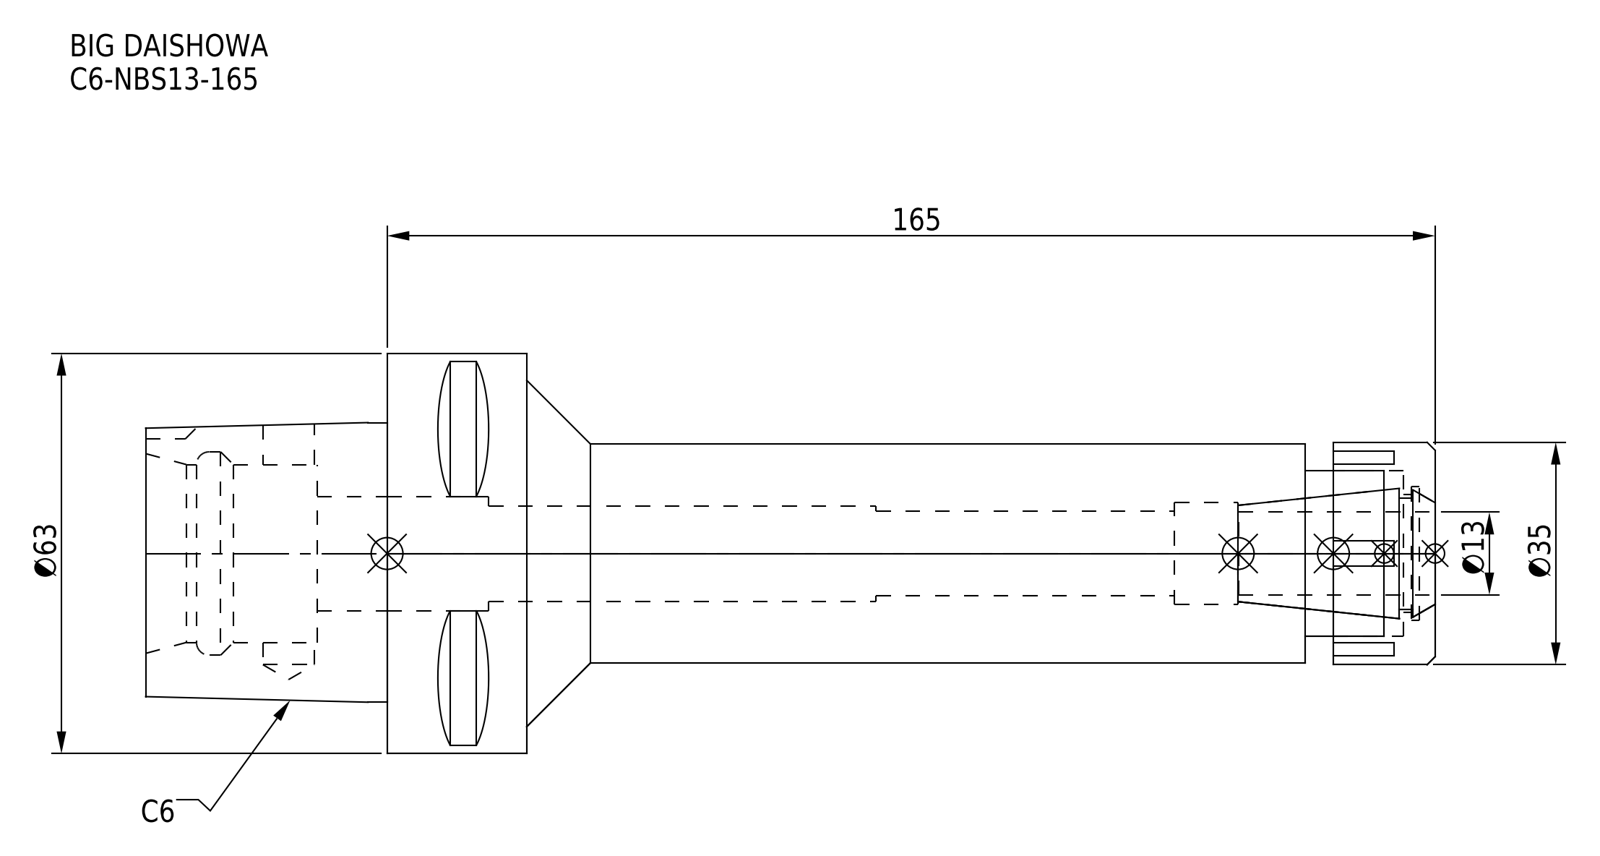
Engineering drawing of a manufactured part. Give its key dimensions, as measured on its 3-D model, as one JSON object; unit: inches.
{"part_name": "C6-NBS13-165-FreeParts; C6-NBS13-165.stp; C6-NBS13-165_1.stp; NBN13_1.stp (+3 more)", "step_written_by": "SolidWorks 2019 (CONFIG_CONTROL_DESIGN)", "units": "inches", "bodies": {"solids": 2, "faces": 112, "planar": 61, "cylindrical": 33, "other": 18}, "overall_size": [7.992, 2.48, 2.48], "volume_in3": 12.62, "surface_area_in2": 69.66, "round_holes": [[0.319, 1], [0.524, 1], [0.591, 1], [0.63, 1], [0.709, 1], [0.728, 1], [0.827, 1], [1.024, 1], [1.102, 1], [1.26, 1]], "round_bosses_or_shafts": [[2.48, 1], [1.378, 1], [1.358, 1]], "partial_cylinders_radius": [[0.197, 1]], "face_to_face_distances": [0.866, 5.63, 6.496, 0.433, 6.299, 7.992, 2.362, 1.496, 0.807, 0.63]}
